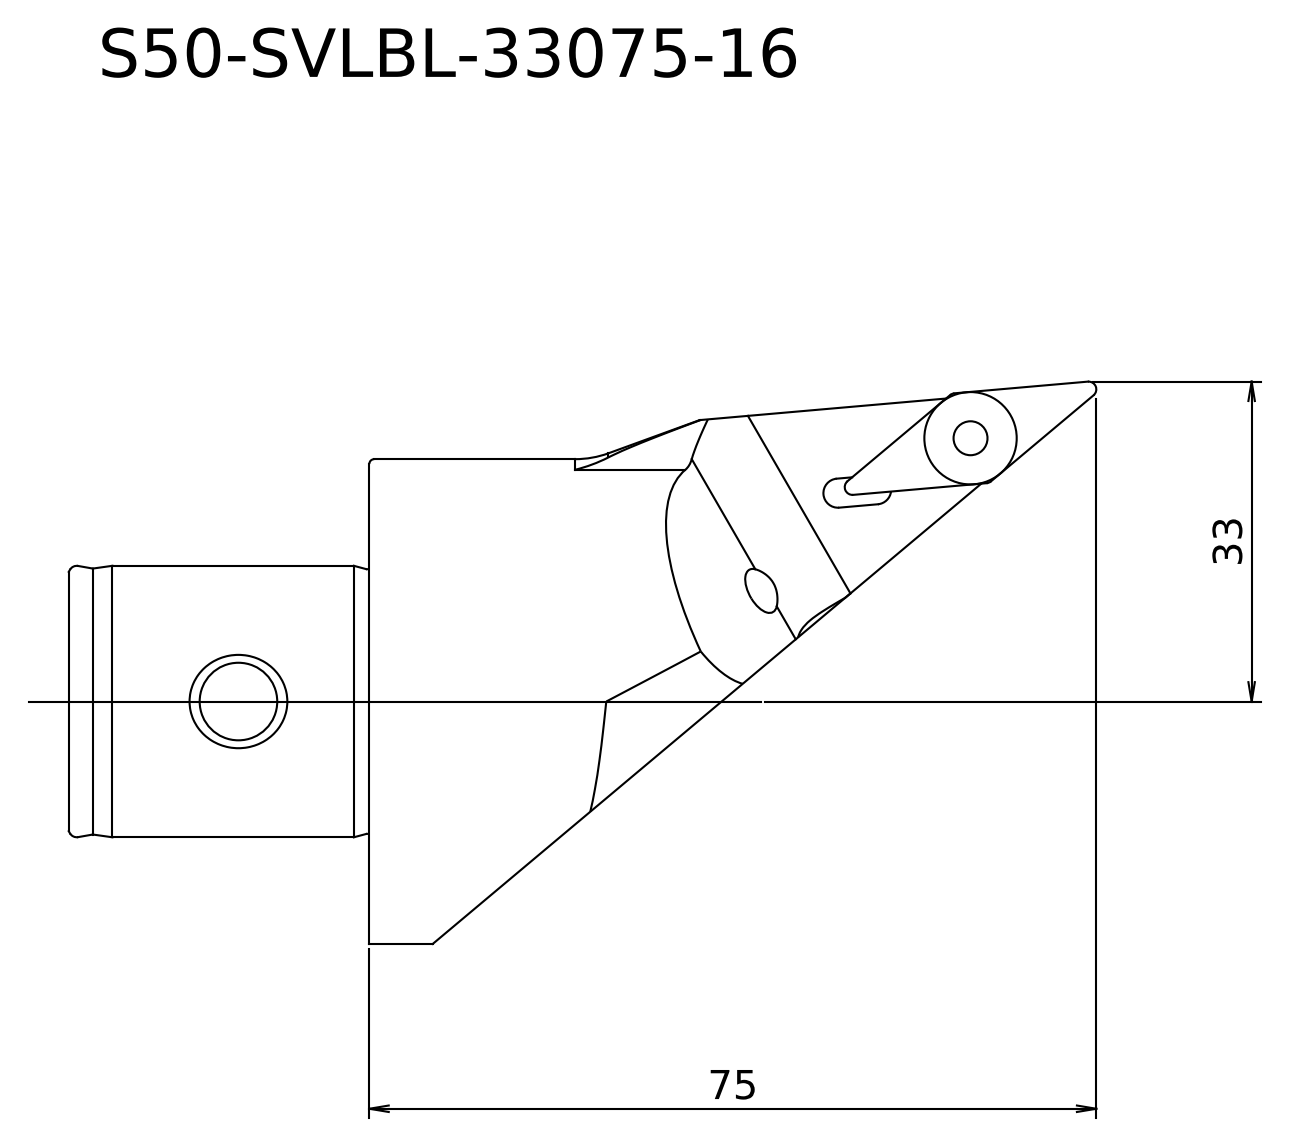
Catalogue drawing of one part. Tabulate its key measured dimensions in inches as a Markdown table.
| quantity | value |
| --- | --- |
| STEP written by | Kubotek KeyCreator V8.5.1 (14335) (CONFIG_CONTROL_DESIGN) |
| units | inches |
| bodies | 1 solid, 32 faces (14 planar, 12 cylindrical, 6 other) |
| overall size | 2.949 × 2.283 × 2.087 |
| volume | 4.491 in³ |
| surface area | 17.42 in² |
| round bosses / shafts (diameter × count) | 1.969 × 1 |
| partial cylindrical surfaces (radius × count) | 0.394 × 2, 0.016 × 1, 0.031 × 1, 0.197 × 1, 0.315 × 1, 1.535 × 1, 1.969 × 1 |
| main face-to-face distances | 0.019, 0.199, 0.187, 0.375, 0.356, 0.356, 0.375, 1.114, 1.102, 0.915 |
